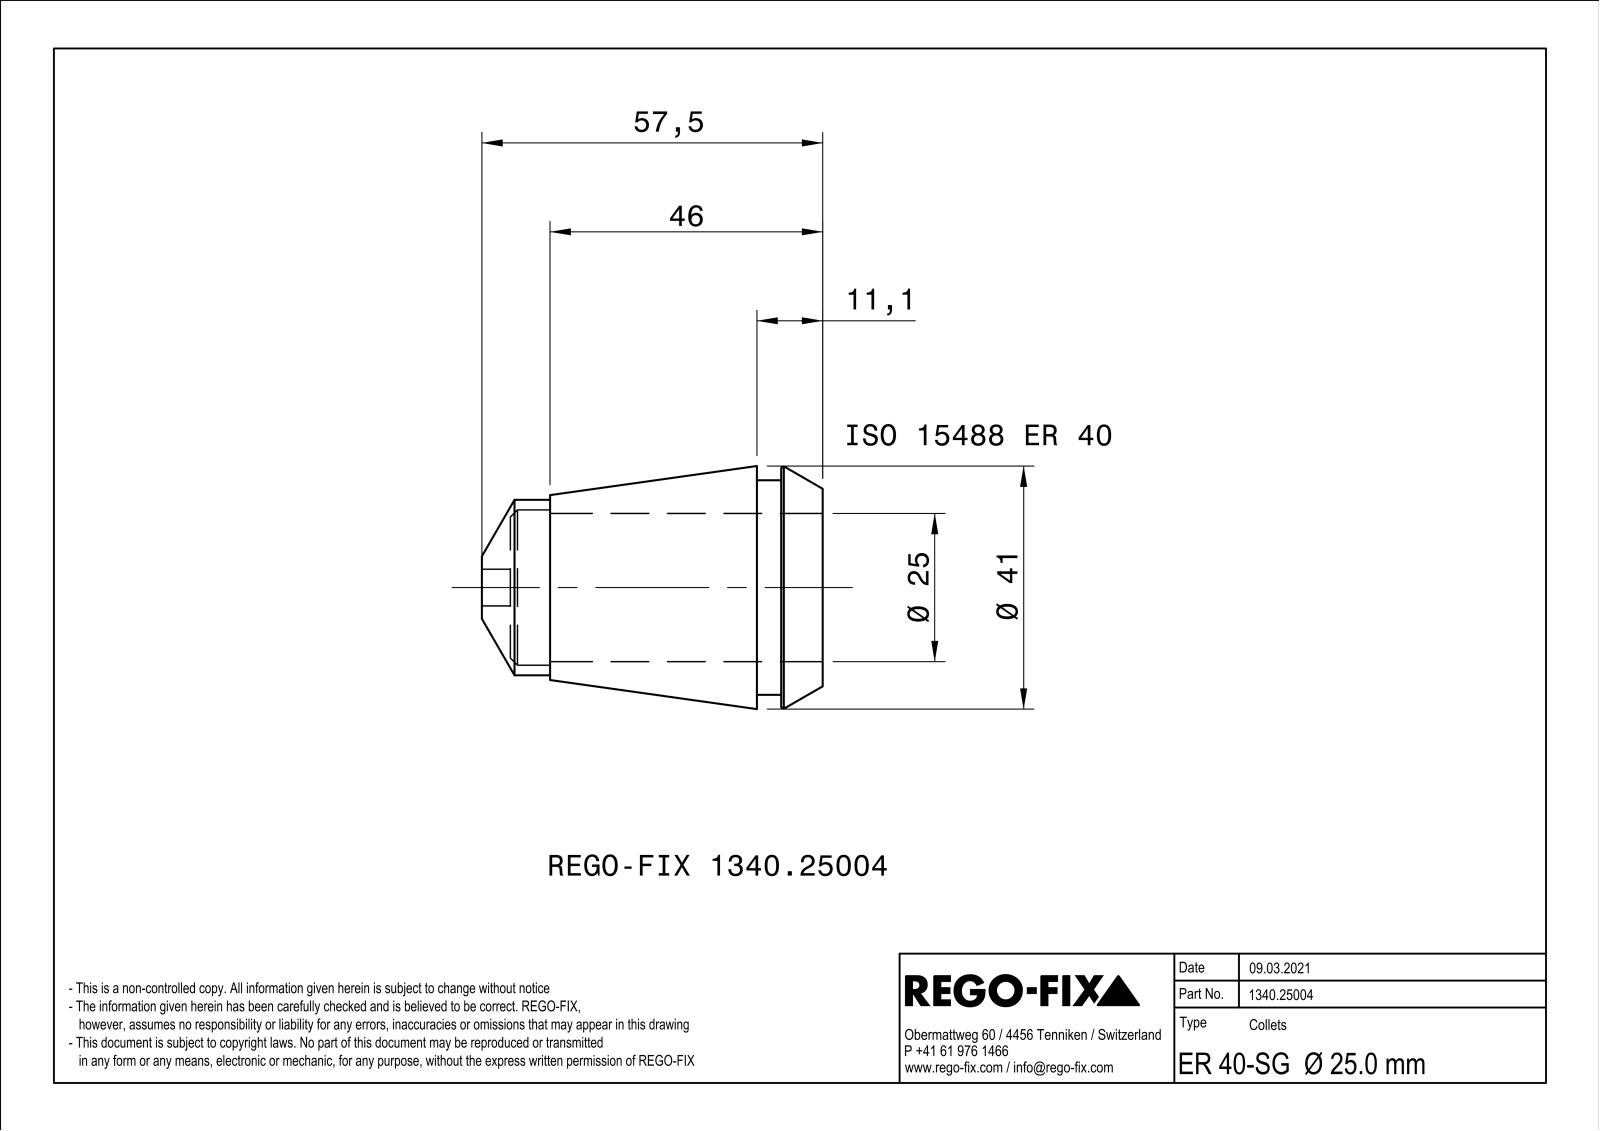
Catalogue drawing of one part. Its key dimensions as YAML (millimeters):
part_name: "NOCUT"
step_written_by: "SIEMENS PLM Software Solid Edge ST10 (AUTOMOTIVE_DESIGN)"
units: millimeters
bodies: {solids: 1, faces: 300, planar: 148, cylindrical: 48, other: 104}
overall_size: [61.8, 40.85, 40.85]
volume: 24720
surface_area: 17731
round_holes:
  - {diameter: 3, count: 1}
  - {diameter: 25, count: 1}
  - {diameter: 26, count: 1}
  - {diameter: 26.2, count: 1}
round_bosses_or_shafts:
  - {diameter: 36.2, count: 1}
  - {diameter: 29.6, count: 1}
  - {diameter: 7, count: 1}
  - {diameter: 4.4, count: 1}
partial_cylinders:
  - {radius: 3.09, count: 1}
  - {radius: 14.1, count: 1}
  - {radius: 14.45, count: 1}
face_to_face_distances: [1, 52.7, 7, 45.7, 11.1, 4.1, 41.6, 6.7, 46, 39]
